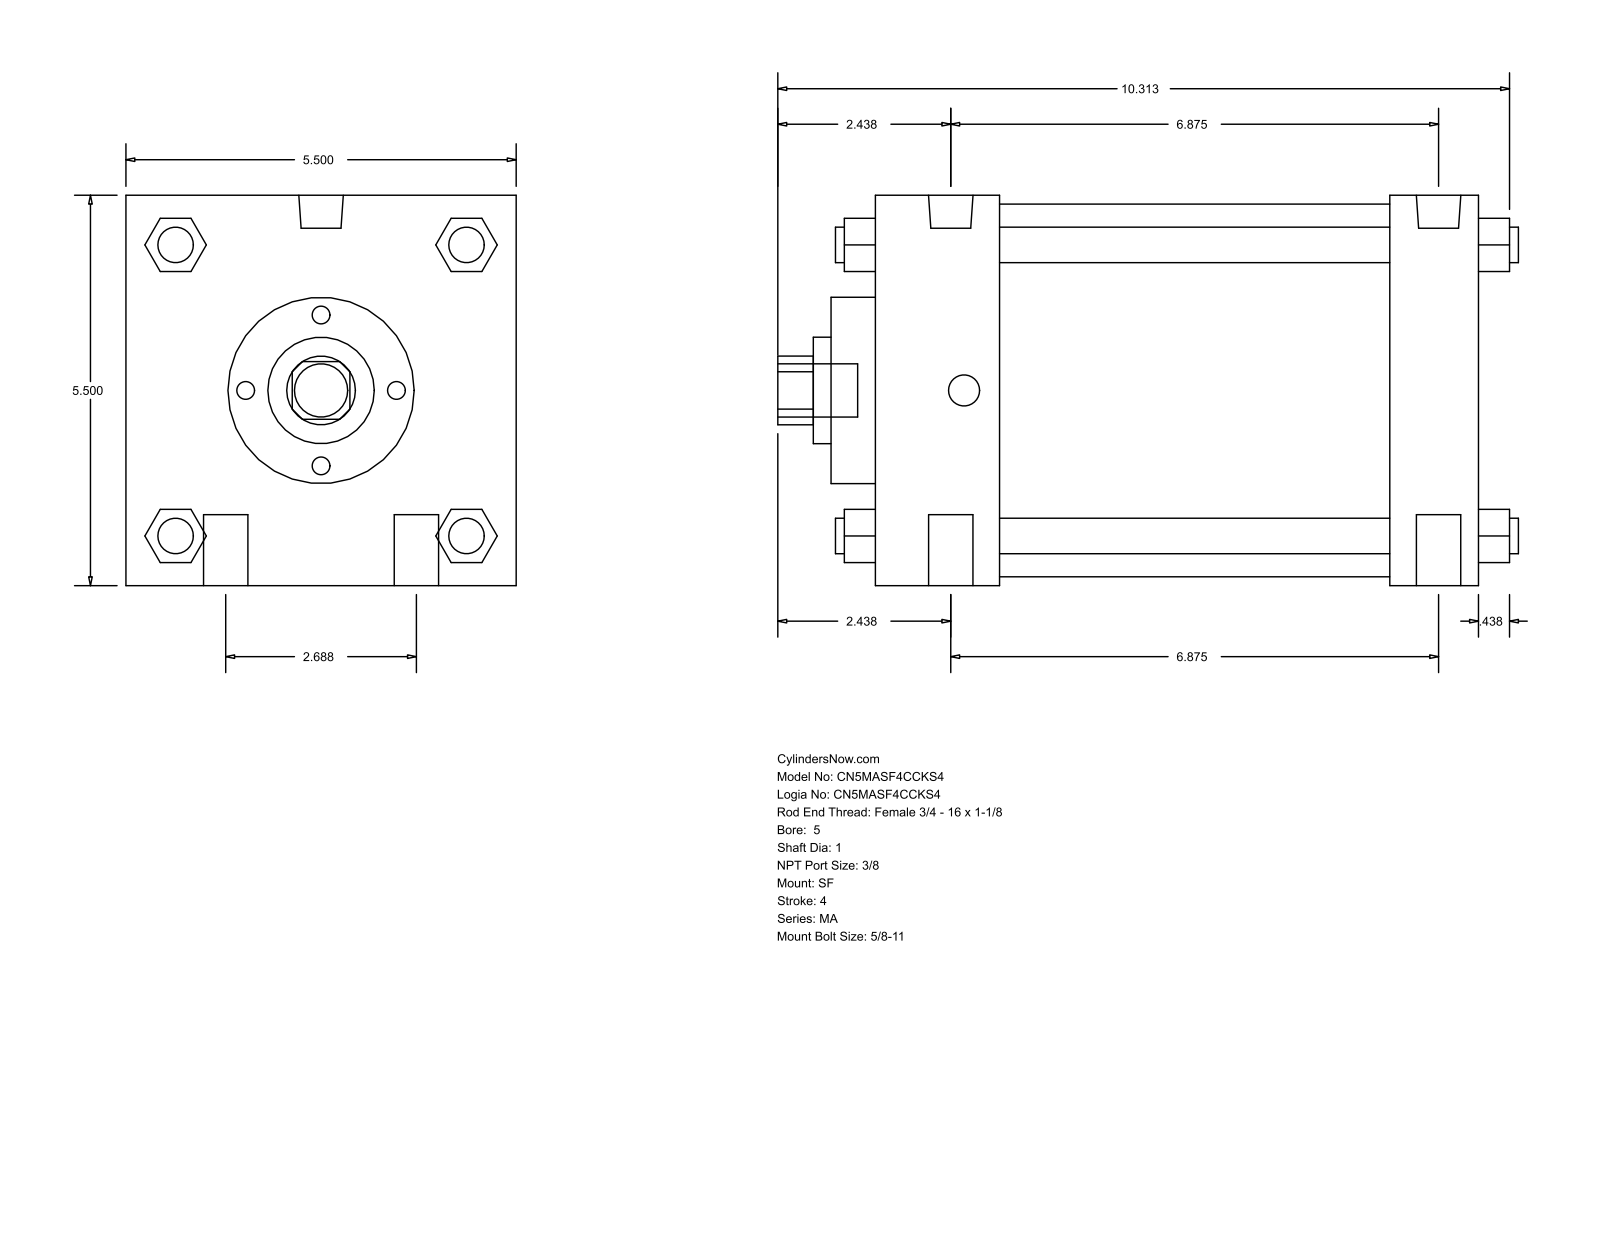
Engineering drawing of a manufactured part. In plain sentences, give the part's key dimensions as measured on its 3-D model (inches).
The part is named "MA_SF__0500_1". Its 3-D file was written by "GSSL Pune (CONFIG_CONTROL_DESIGN)". It is 0 solids with 126 faces: 95 planar, 31 cylindrical and 0 other. Overall it measures 10.437 by 5.5 by 5.5 inches. Round holes: 1 of diameter 1, 1 of diameter 1.5, 1 of diameter 2.625, 1 of diameter 5.25. Round bosses or shafts: 4 of diameter 0.625, 4 of diameter 0.5, 2 of diameter 0.627, 2 of diameter 0.437, 1 of diameter 0.75. Partial cylindrical surfaces (rounded edges, fillets, slot ends): 1 of radius 0.484. The main face-to-face distances are 5.5, 8.5, 1.75, 7.25, 5.5, 6.75, 1.25, 0.625, 2.375, 7.875.
